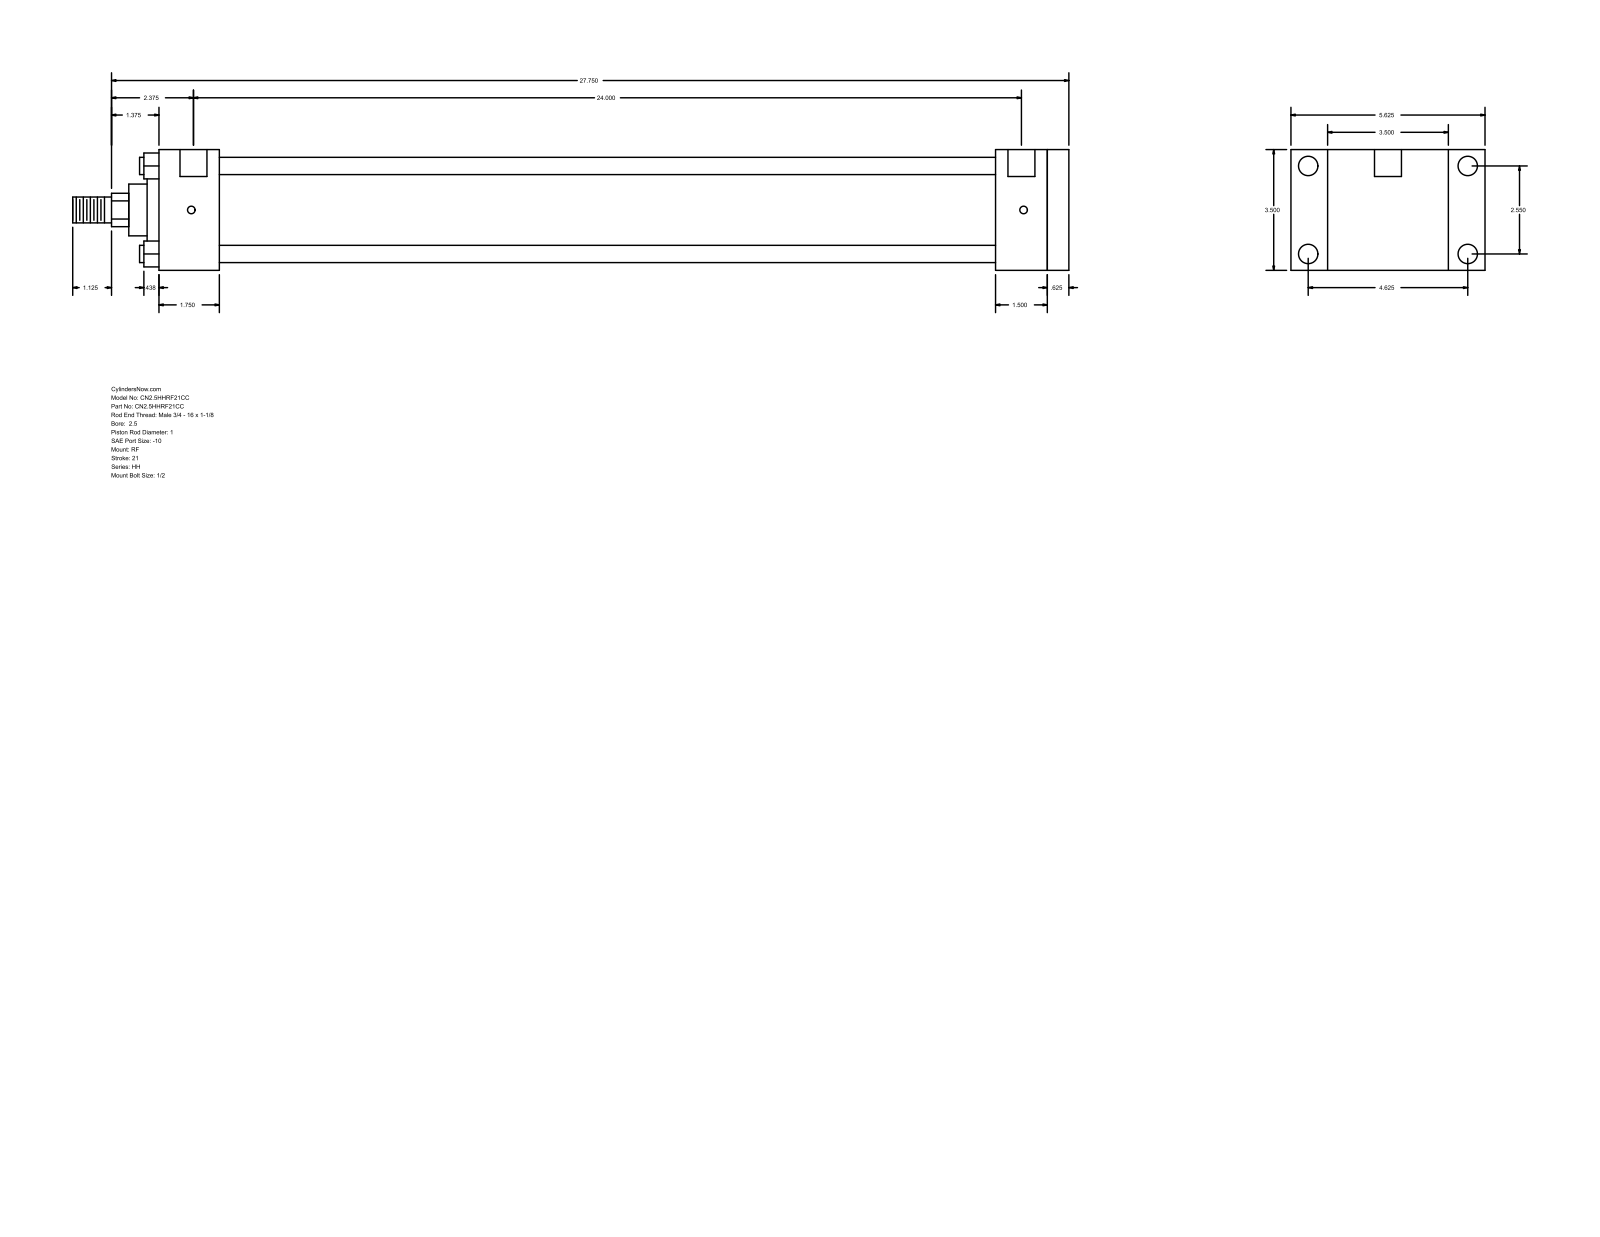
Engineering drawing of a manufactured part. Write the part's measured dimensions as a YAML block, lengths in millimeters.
part_name: "HH_RF__0250_1"
step_written_by: "GSSL Pune (CONFIG_CONTROL_DESIGN)"
units: millimeters
bodies: {solids: 0, faces: 94, planar: 65, cylindrical: 29, other: 0}
overall_size: [733.42, 142.88, 88.9]
round_holes:
  - {diameter: 5.56, count: 4}
  - {diameter: 14.3, count: 4}
  - {diameter: 19.84, count: 2}
round_bosses_or_shafts:
  - {diameter: 12.7, count: 4}
  - {diameter: 73.03, count: 1}
  - {diameter: 60.33, count: 1}
  - {diameter: 38.1, count: 1}
  - {diameter: 25.4, count: 1}
  - {diameter: 19.05, count: 1}
partial_cylinders:
  - {radius: 12.29, count: 1}
face_to_face_distances: [88.9, 15.87, 654.06, 669.93, 38.1, 44.46, 609.6, 625.47, 615.96, 571.5]
hole_center_spacings: [1.59, 64.76, 117.48, 134.15, 611.18, 612.77, 609.59]
